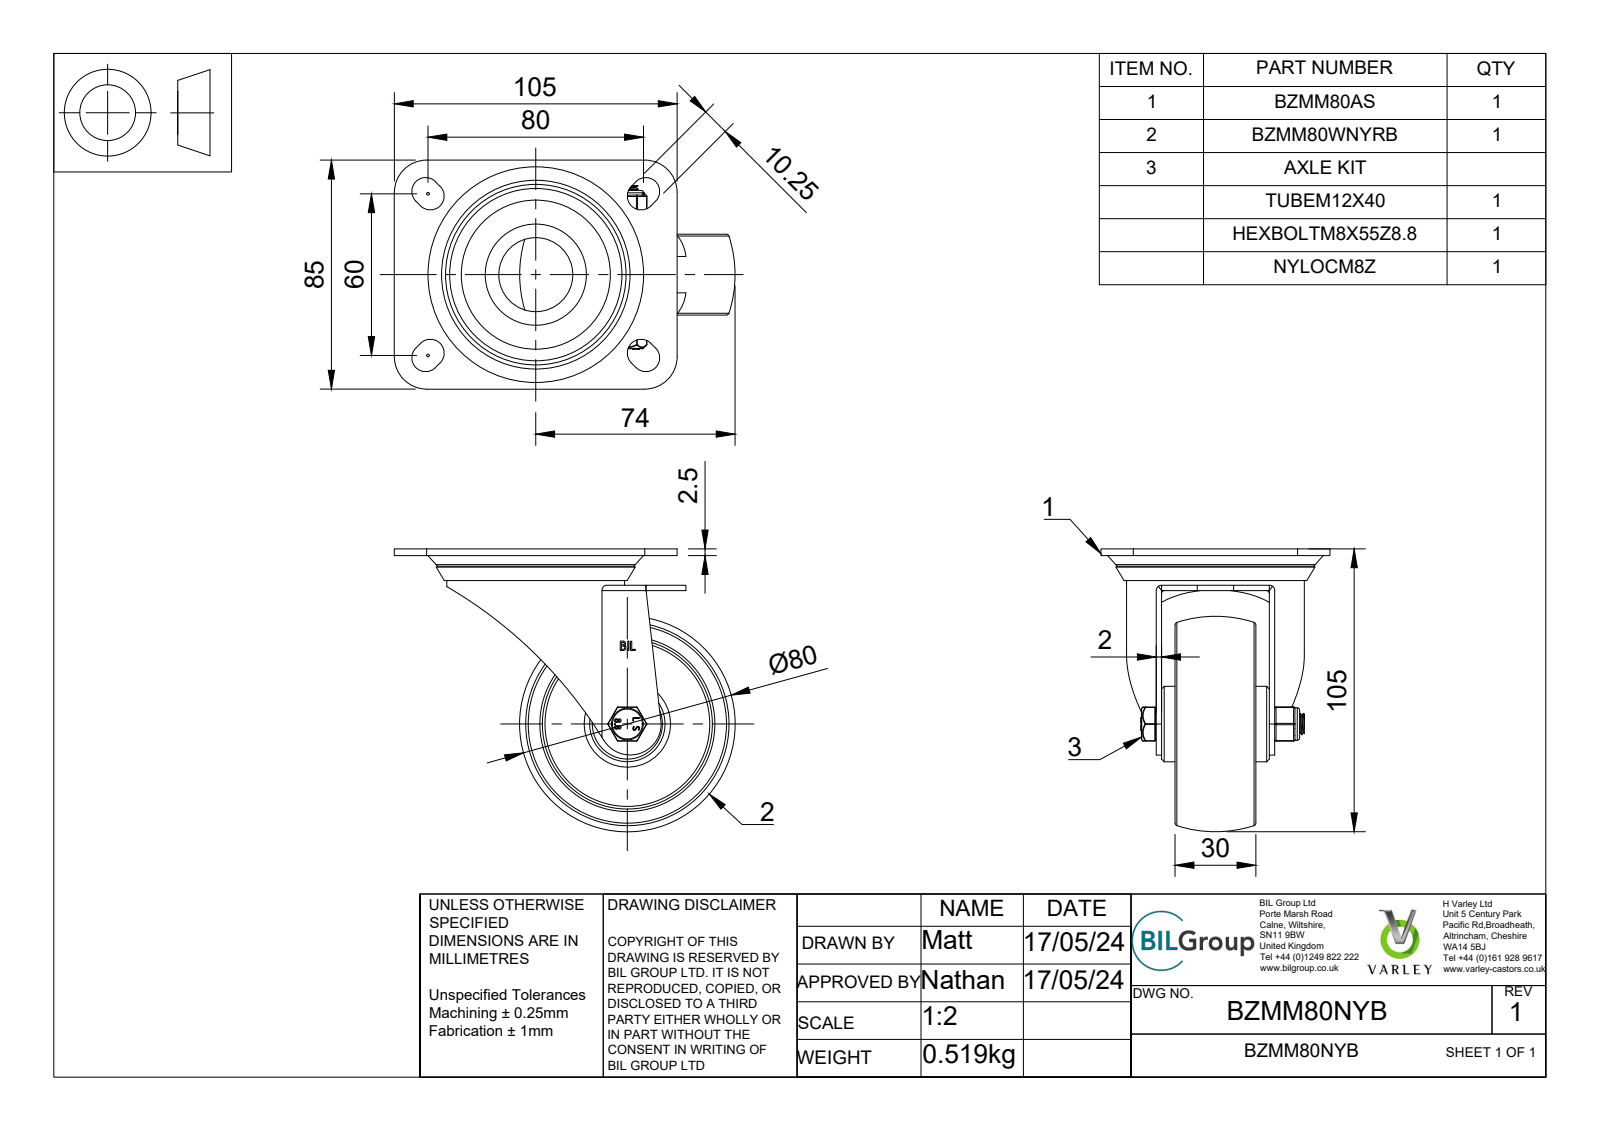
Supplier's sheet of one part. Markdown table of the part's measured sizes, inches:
| quantity | value |
| --- | --- |
| part name | BZMM80NYB v4; BZMM80AS - 2 v1; ZINC PLATED, PRESSED STEEL TOP PLATE 1; ZINC PLATED, PRESSED STEEL TOP PLATE 1 Geometry (+7 more) |
| STEP written by | Autodesk Translation Framework v13.14.0.145 (AUTOMOTIVE_DESIGN) |
| units | inches |
| bodies | 42 solids, 492 faces (189 planar, 183 cylindrical, 120 other) |
| overall size | 4.98 × 4.134 × 3.346 |
| volume | 8.128 in³ |
| surface area | 132.8 in² |
| round holes (diameter × count) | 0.026 × 2, 0.315 × 1, 0.323 × 1, 0.331 × 1, 0.339 × 1, 0.488 × 1, 0.492 × 1, 0.906 × 1, 1.083 × 1, 1.89 × 1, 2.441 × 1 |
| round bosses / shafts (diameter × count) | 0.148 × 8, 2.598 × 1, 1.24 × 1, 1.102 × 1, 0.768 × 1, 0.476 × 1, 0.469 × 1, 0.453 × 1 |
| partial cylindrical surfaces (radius × count) | 0.02 × 18, 0.01 × 12, 0.202 × 8, 0.013 × 4, 0.025 × 4, 0.039 × 4, 0.472 × 4, 0.025 × 2 |
| main face-to-face distances | 0.079, 0.098, 0.197, 0.512, 0.709, 0.866, 0.276, 0.157, 0.787, 0.945 |
| hole center spacings | 0.127, 0.098 |
